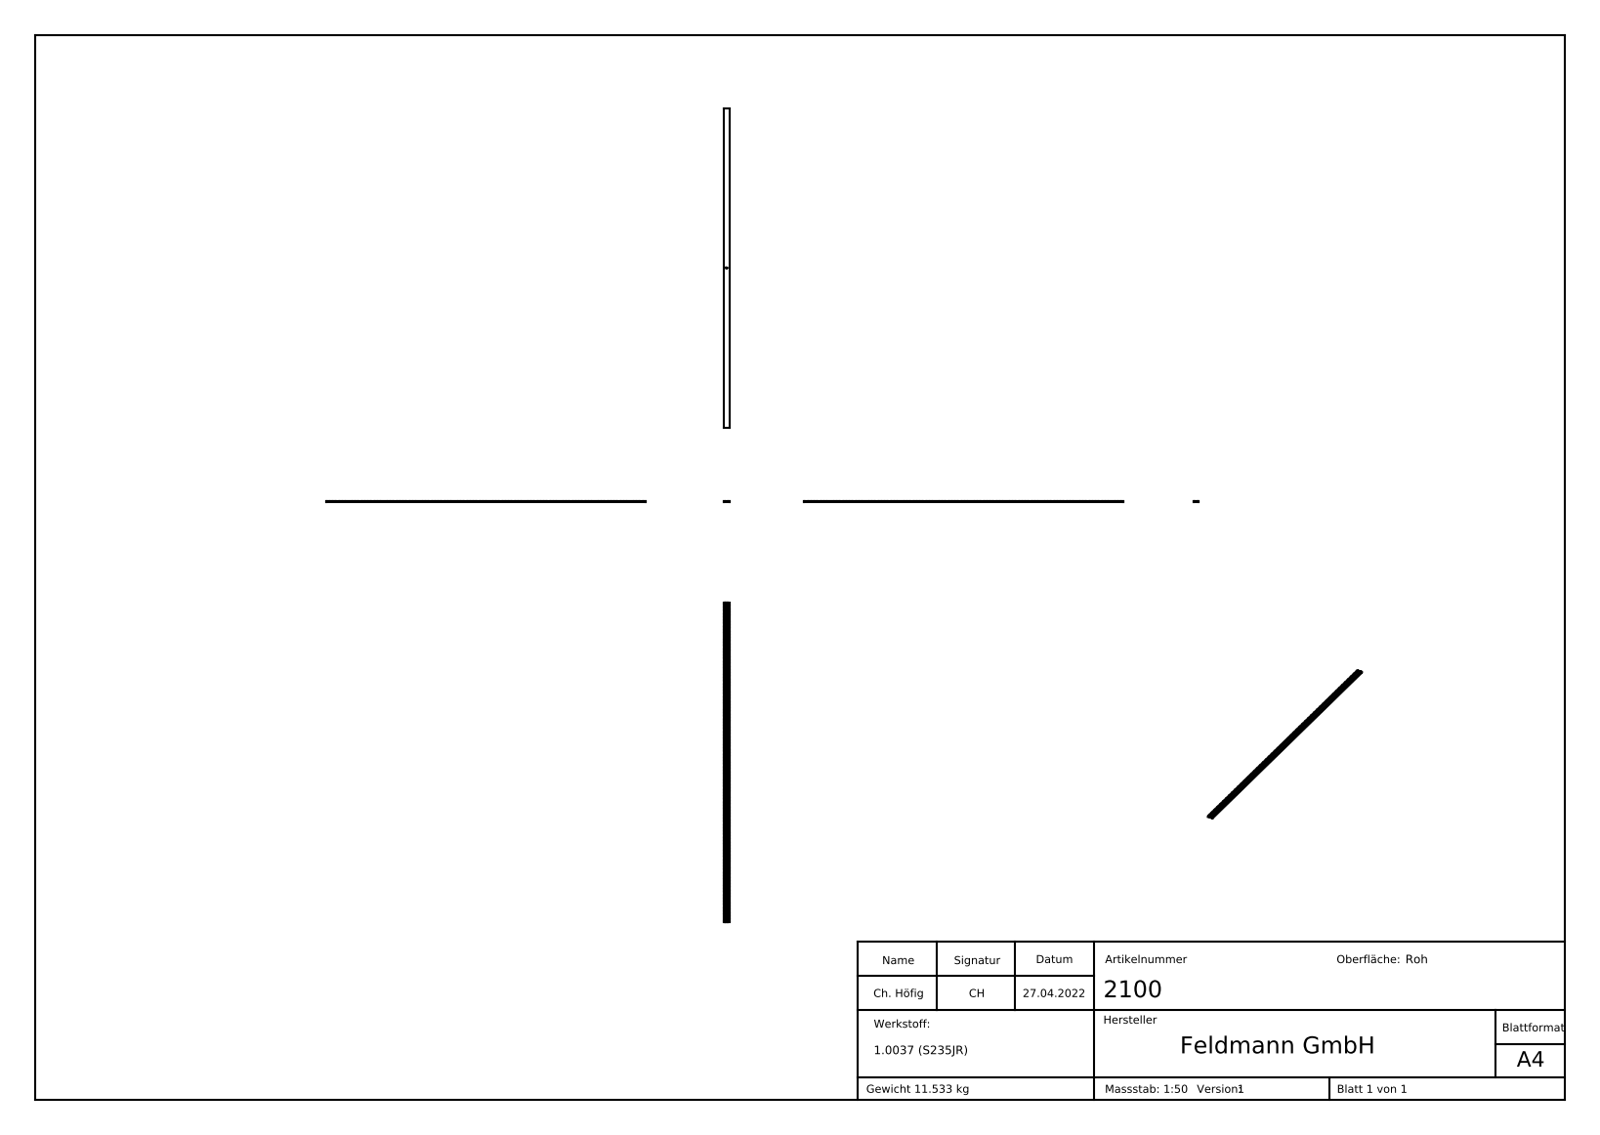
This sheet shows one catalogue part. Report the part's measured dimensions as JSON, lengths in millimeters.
{"part_name": "2100", "step_written_by": "SolidWorks 2018 (CONFIG_CONTROL_DESIGN)", "units": "millimeters", "bodies": {"solids": 1, "faces": 411, "planar": 118, "cylindrical": 0, "other": 293}, "overall_size": [3000, 50, 10], "volume_mm3": 1479000, "surface_area_mm2": 362914, "face_to_face_distances": [10, 50, 18.38, 3000, 9.9, 1.82, 1.64, 0.34, 1500, 23.99]}
